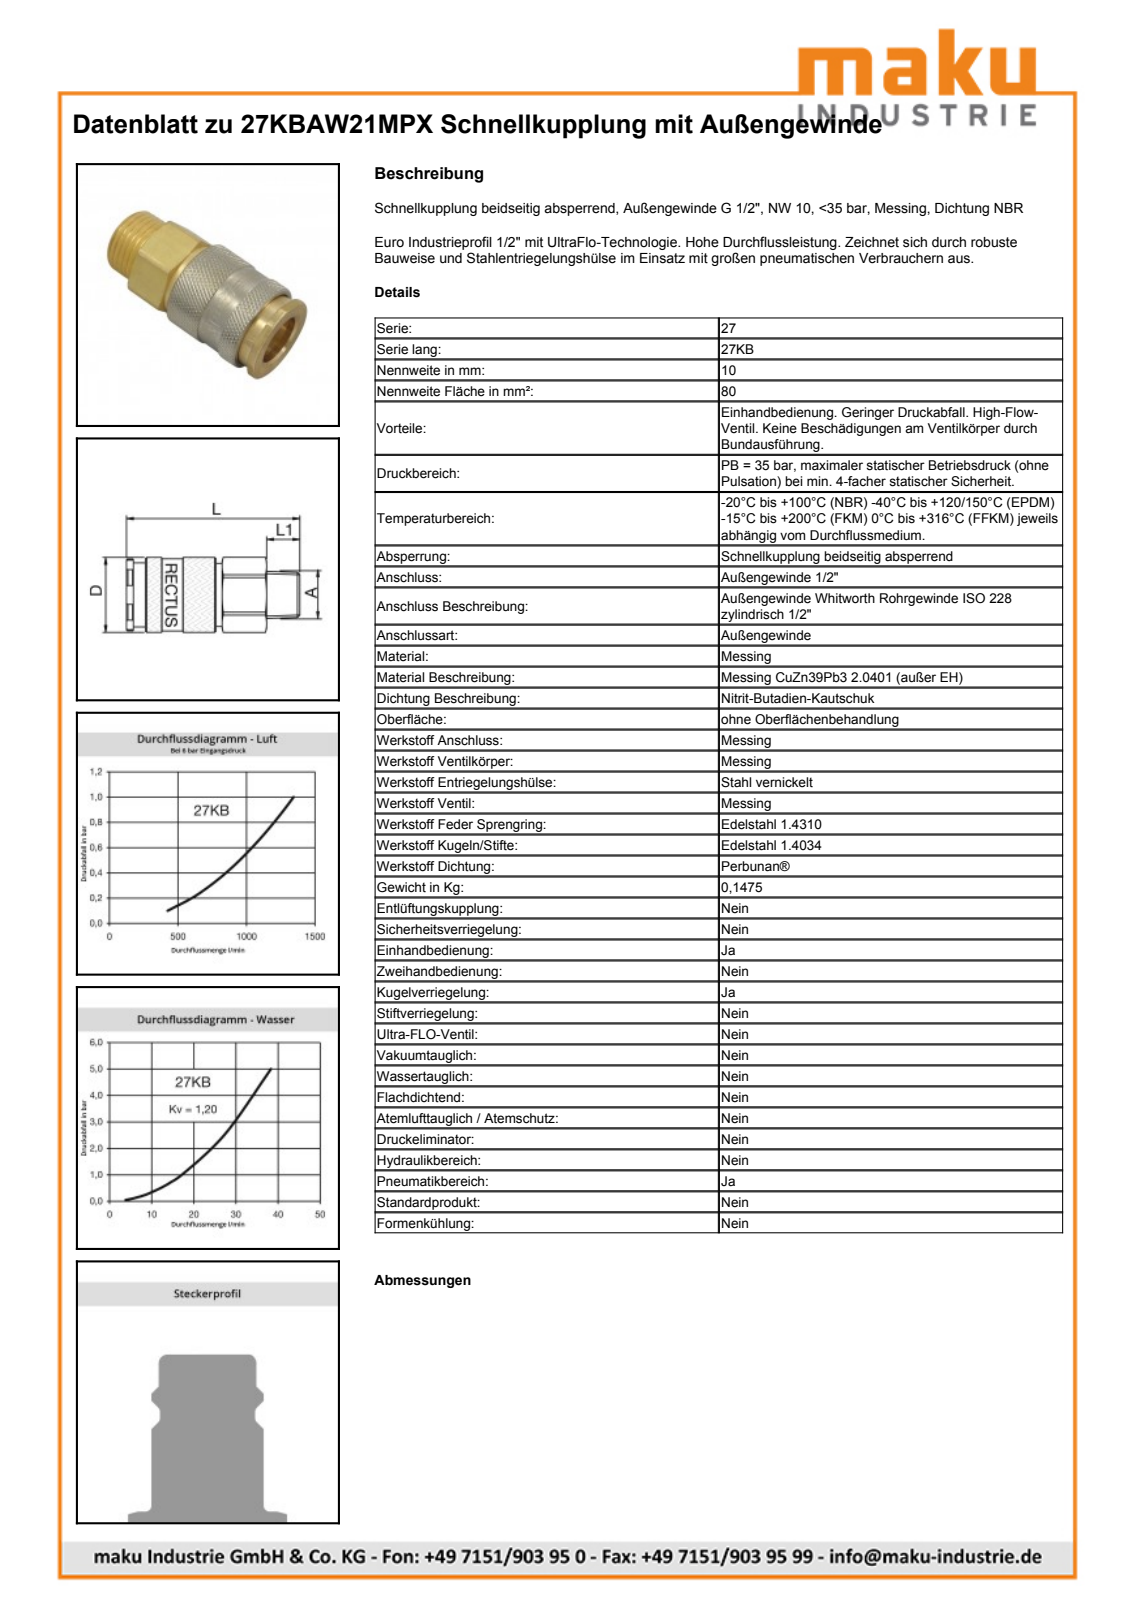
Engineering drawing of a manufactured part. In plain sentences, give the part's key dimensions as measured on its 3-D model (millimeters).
The part is named "D108511". Its 3-D file was written by "Autodesk Inventor 2013 (AUTOMOTIVE_DESIGN)". It is 2 solids with 659 faces: 227 planar, 83 cylindrical and 349 other. Overall it measures 59.45 by 27.15 by 27.15 millimeters. Its volume is 26 857 cubic millimeters and its surface area 10 611 square millimeters. Round holes: 1 of diameter 19, 1 of diameter 20.3, 1 of diameter 20.95, 1 of diameter 23.35, 1 of diameter 23.55. Round bosses or shafts: 1 of diameter 27.15, 1 of diameter 26, 1 of diameter 23.1, 1 of diameter 22.75, 1 of diameter 20.96, 1 of diameter 20, 1 of diameter 18.8, 1 of diameter 18.7. Partial cylindrical surfaces (rounded edges, fillets, slot ends): 1 of radius 9.9, 1 of radius 12.9, 1 of radius 13.53. The main face-to-face distances are 24, 59.45, 24.02, 24.95, 32, 32.3, 27.15, 47.45, 15.15, 12.
